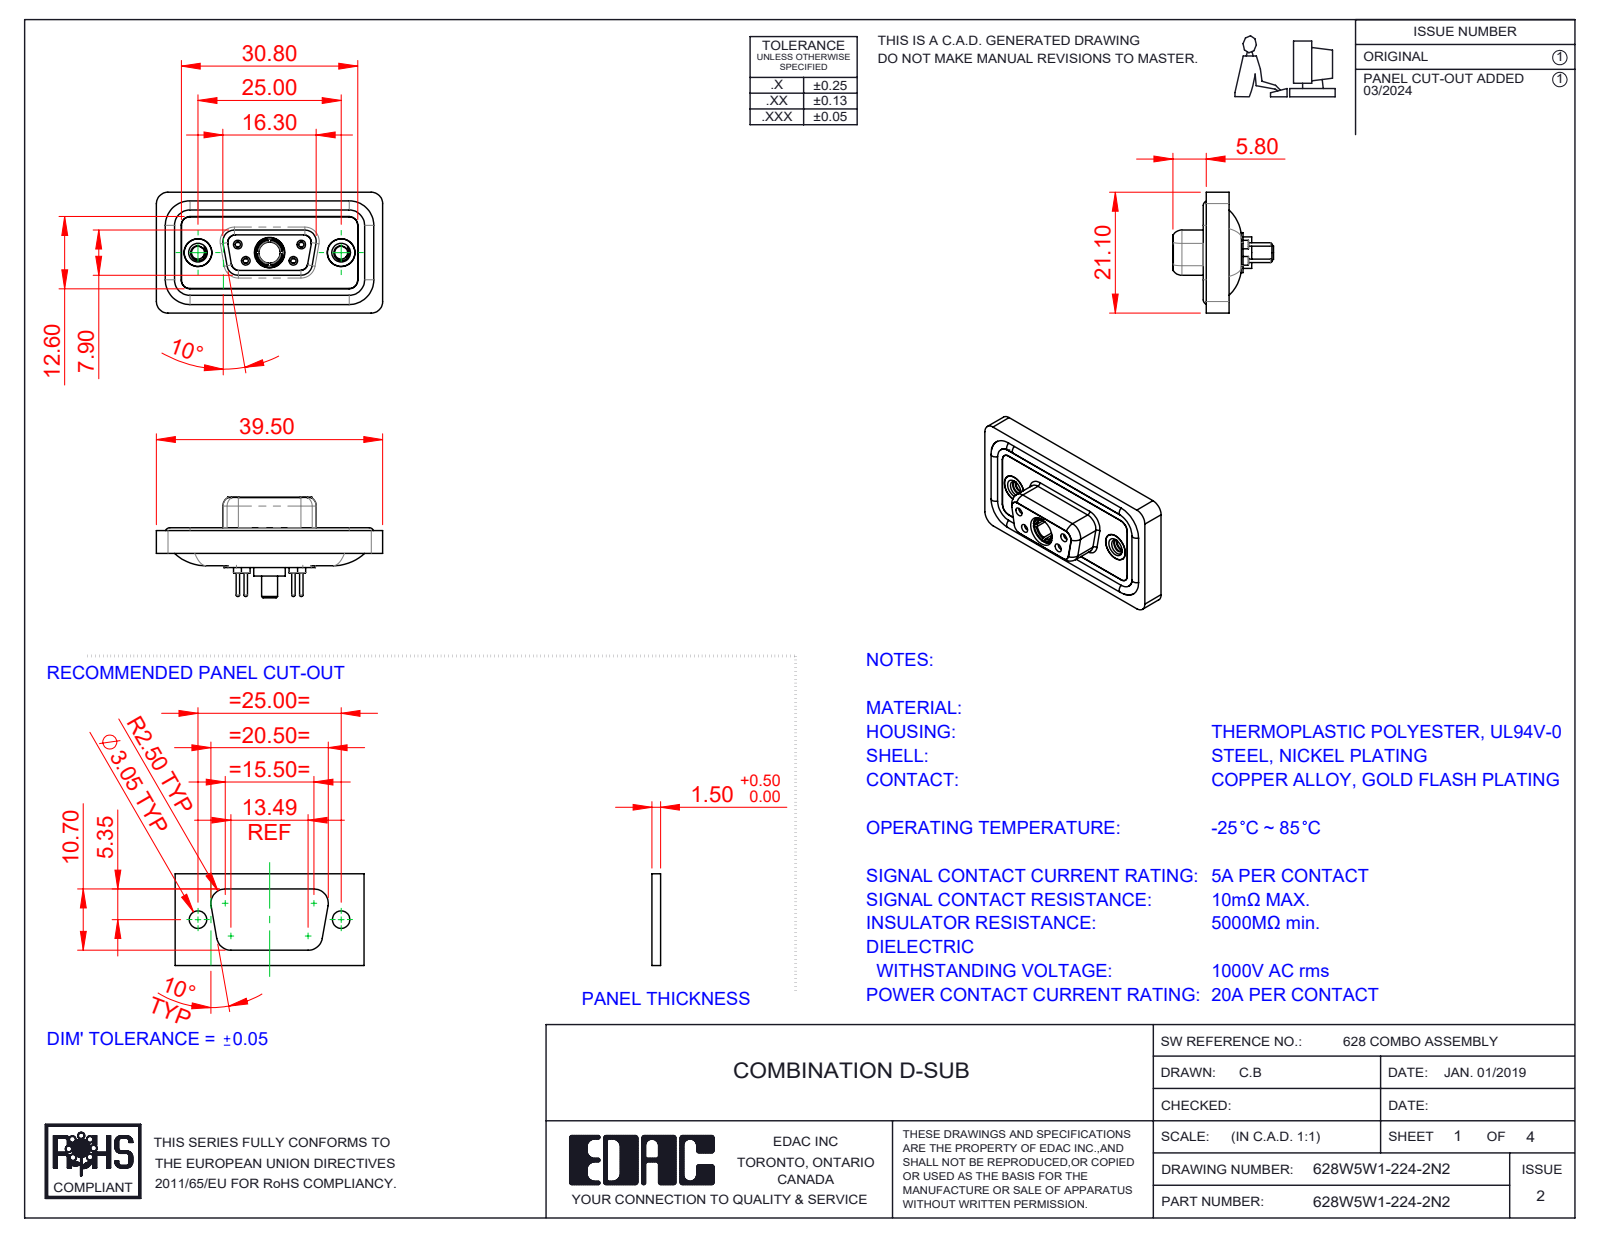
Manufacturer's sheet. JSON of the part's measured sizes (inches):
{"part_name": "628Combo Waterproof Housing_09 Contacts; 628Combo Contact Row 1_24; 628Combo Contact Row 2_24; 628Combo Threaded Rivet_2 (+5 more)", "step_written_by": "SolidWorks 2023 (CONFIG_CONTROL_DESIGN)", "units": "inches", "bodies": {"solids": 13, "faces": 680, "planar": 194, "cylindrical": 287, "other": 199}, "overall_size": [1.555, 0.831, 0.691], "volume_in3": 0.291, "surface_area_in2": 11.83, "round_holes": [[0.035, 4], [0.043, 4], [0.059, 4], [0.079, 4], [0.191, 3], [0.063, 2], [0.067, 2], [0.089, 2], [0.157, 2], [0.159, 2], [0.197, 2], [0.146, 1]], "round_bosses_or_shafts": [[0.063, 6], [0.087, 4], [0.024, 4], [0.195, 2], [0.189, 2], [0.217, 1], [0.205, 1], [0.195, 1]], "partial_cylinders_radius": [[0.059, 22], [0.079, 18], [0.053, 8], [0.063, 8], [0.01, 4], [0.02, 4], [0.024, 4], [0.026, 4]], "face_to_face_distances": [0.016, 0.114, 0.043, 0.071, 0.063, 0.02, 0.222, 0.293, 0.211, 0.26], "hole_center_spacings": [0.124, 0.225, 0.28, 0.492, 0.713, 0.173, 0.173, 0.327]}
